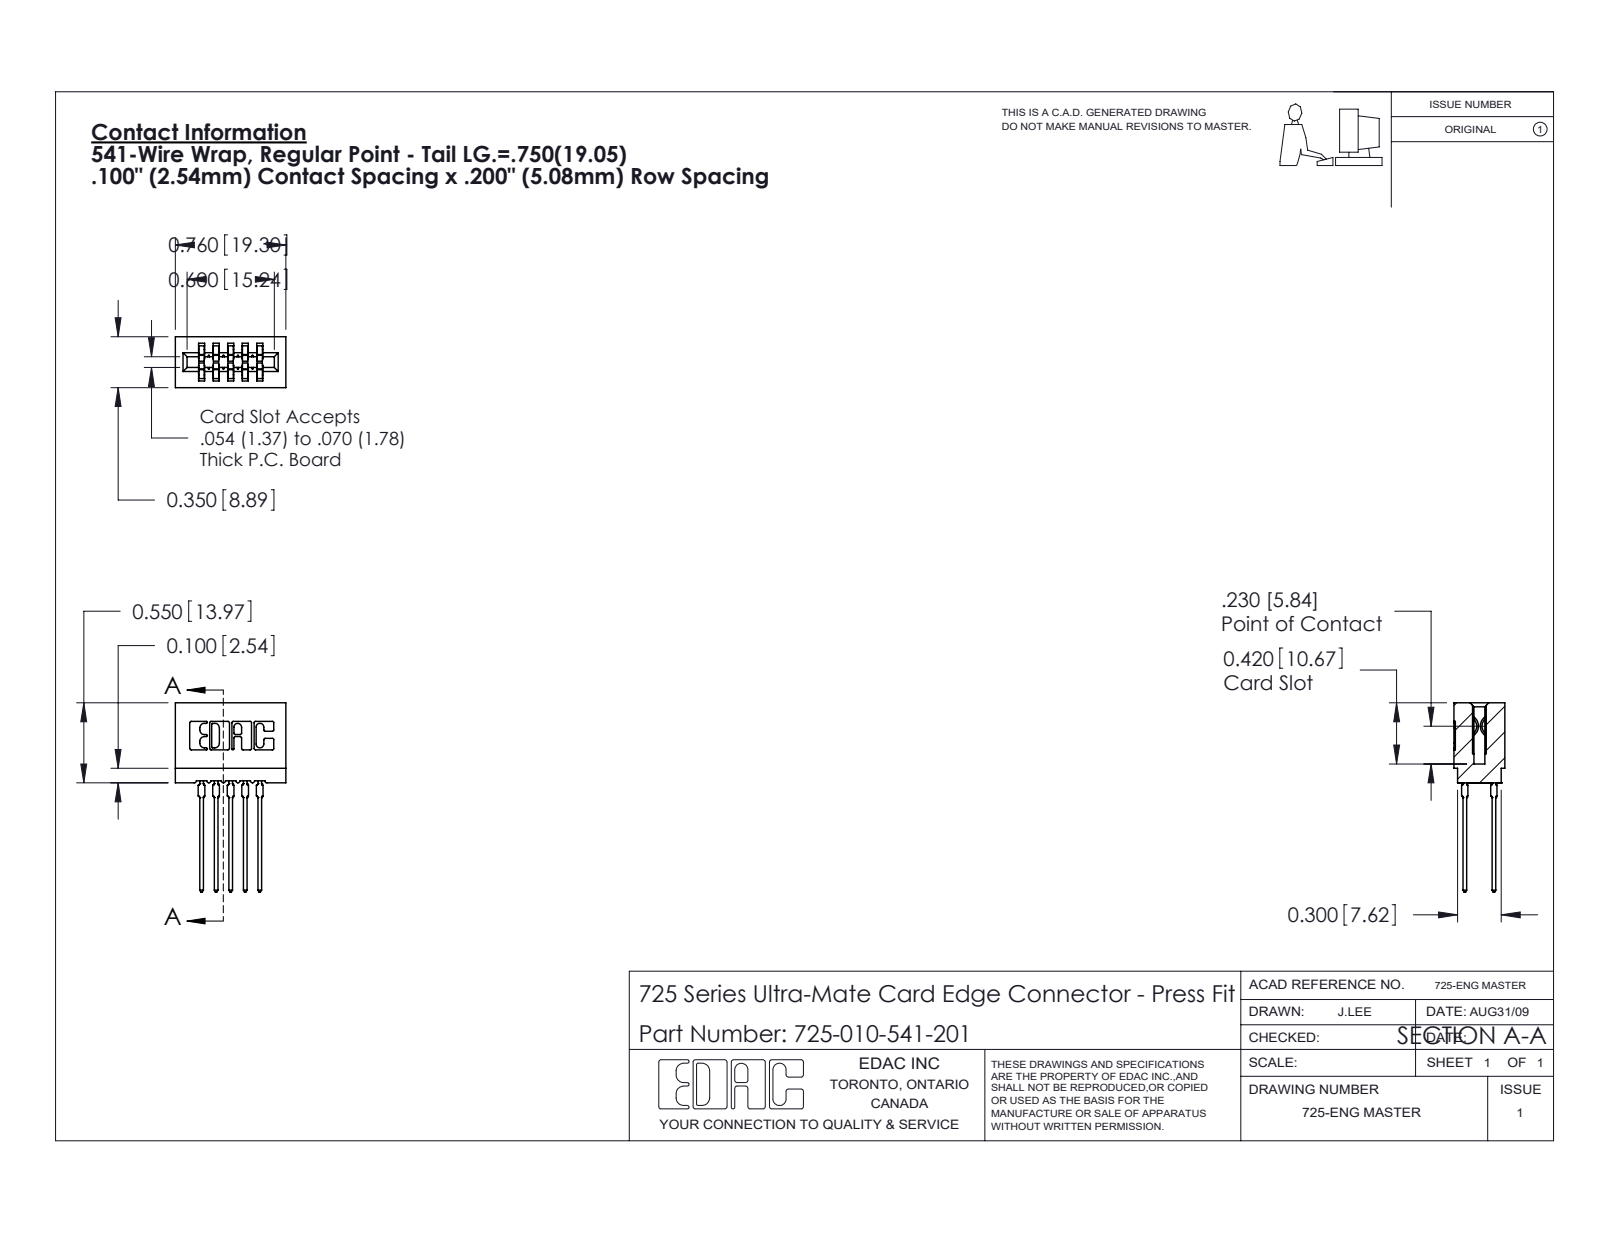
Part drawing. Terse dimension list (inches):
name: 725-010-541-201; 745-292-001_541; 725 Part_Insulator Option - 01
written by: SolidWorks 2020 (CONFIG_CONTROL_DESIGN)
unit: in
bodies: 11 solids, 990 faces (515 planar, 215 cylindrical, 260 other)
size: 1.301 × 0.76 × 0.35
volume: 0.108 in³; area: 4.862 in²
rounds: 22× R0.01, 20× R0.021, 10× R0.015, 8× R0.005, 8× R0.011, 6× R0.007, 6× R0.031, 3× R0.026
face distances: 0.1, 0.2, 0.042, 0.3, 0.142, 0.058, 0.063, 0.287, 0.242, 0.158
